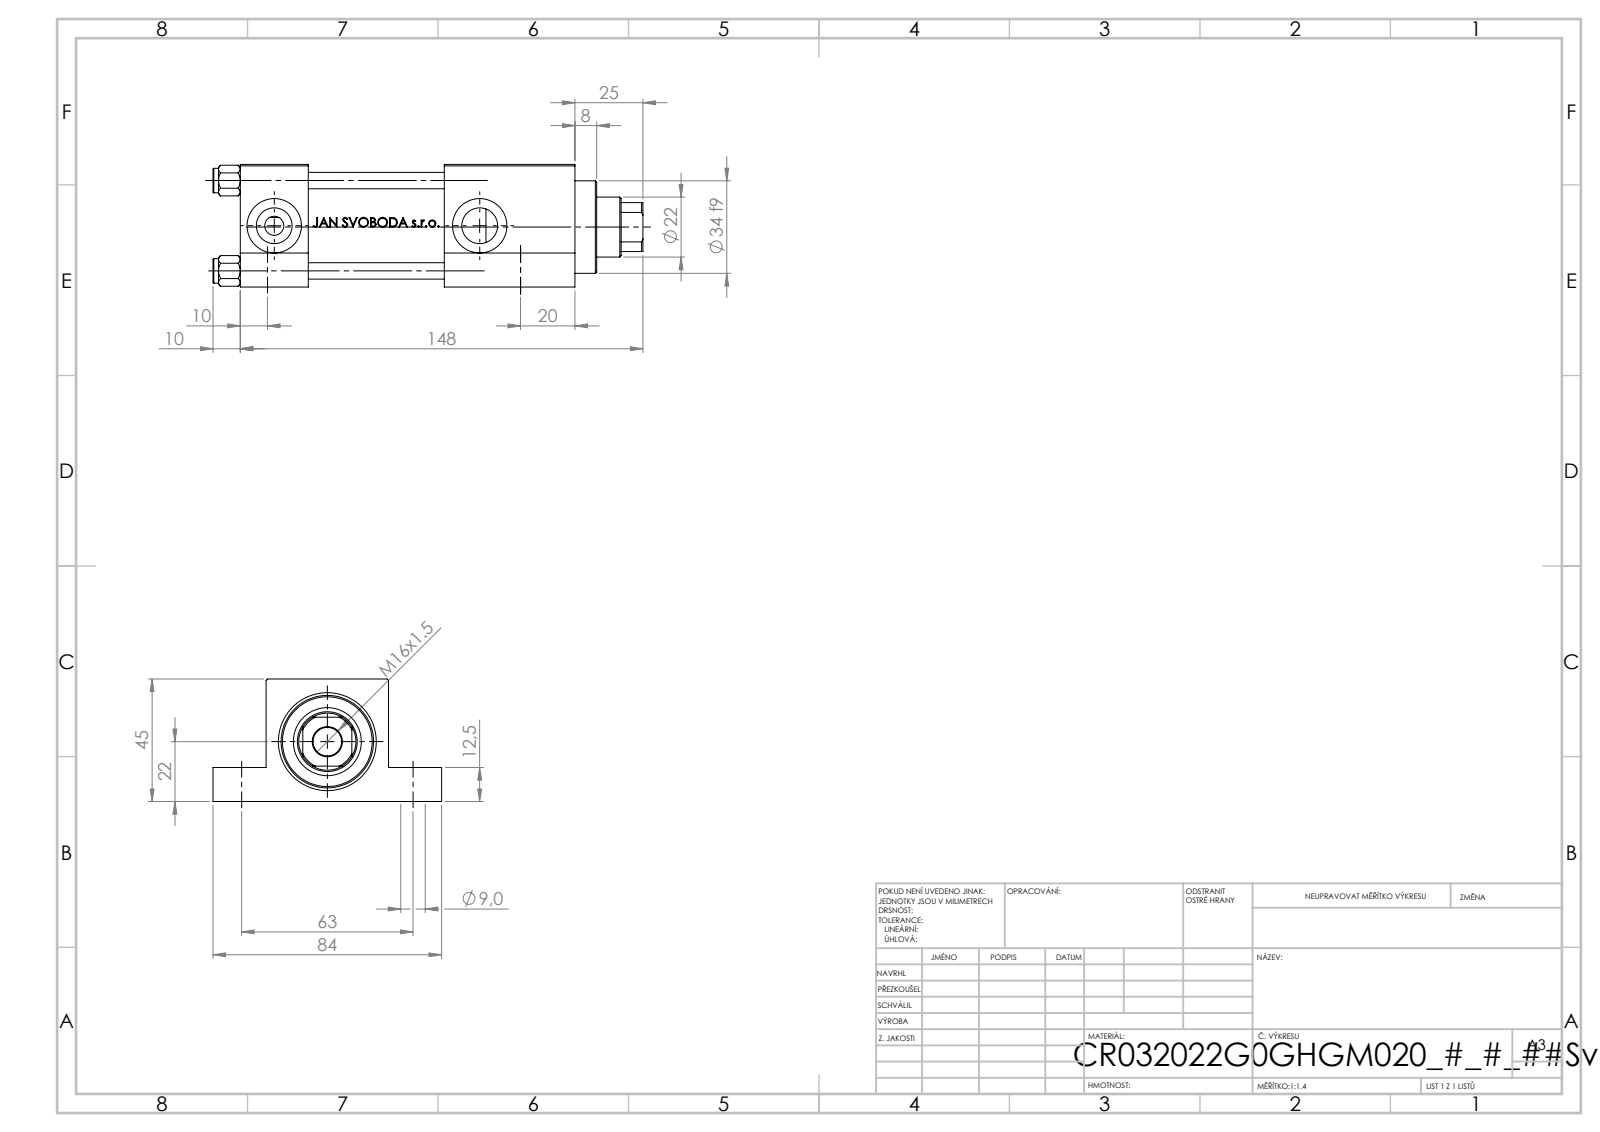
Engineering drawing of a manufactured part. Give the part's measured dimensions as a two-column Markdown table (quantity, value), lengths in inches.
| quantity | value |
| --- | --- |
| part name | V215CR_G_Body; NUT_M5_G; V215CR_VCP_G; V215CR_G_TYCINKA (+1 more) |
| STEP written by | SolidWorks 2019 (CONFIG_CONTROL_DESIGN) |
| units | inches |
| bodies | 11 solids, 1086 faces (430 planar, 124 cylindrical, 532 other) |
| overall size | 6.22 × 3.307 × 1.772 |
| volume | 14.89 in³ |
| surface area | 121.9 in² |
| round holes (diameter × count) | 0.236 × 4, 0.354 × 4, 0.276 × 2, 0.518 × 2, 0.787 × 2, 0.413 × 1, 0.866 × 1, 0.945 × 1, 0.984 × 1, 1.26 × 1, 1.299 × 1 |
| round bosses / shafts (diameter × count) | 0.354 × 4, 1.496 × 1, 1.339 × 1 |
| partial cylindrical surfaces (radius × count) | 0.413 × 1 |
| main face-to-face distances | 1.772, 0.984, 0.492, 1.28, 0.768, 2.539, 4.843, 3.858, 1.969, 2.953 |
| hole center spacings | 1.307, 0.911, 0.938, 1.848, 2.48, 3.661, 4.422, 2.972 |
